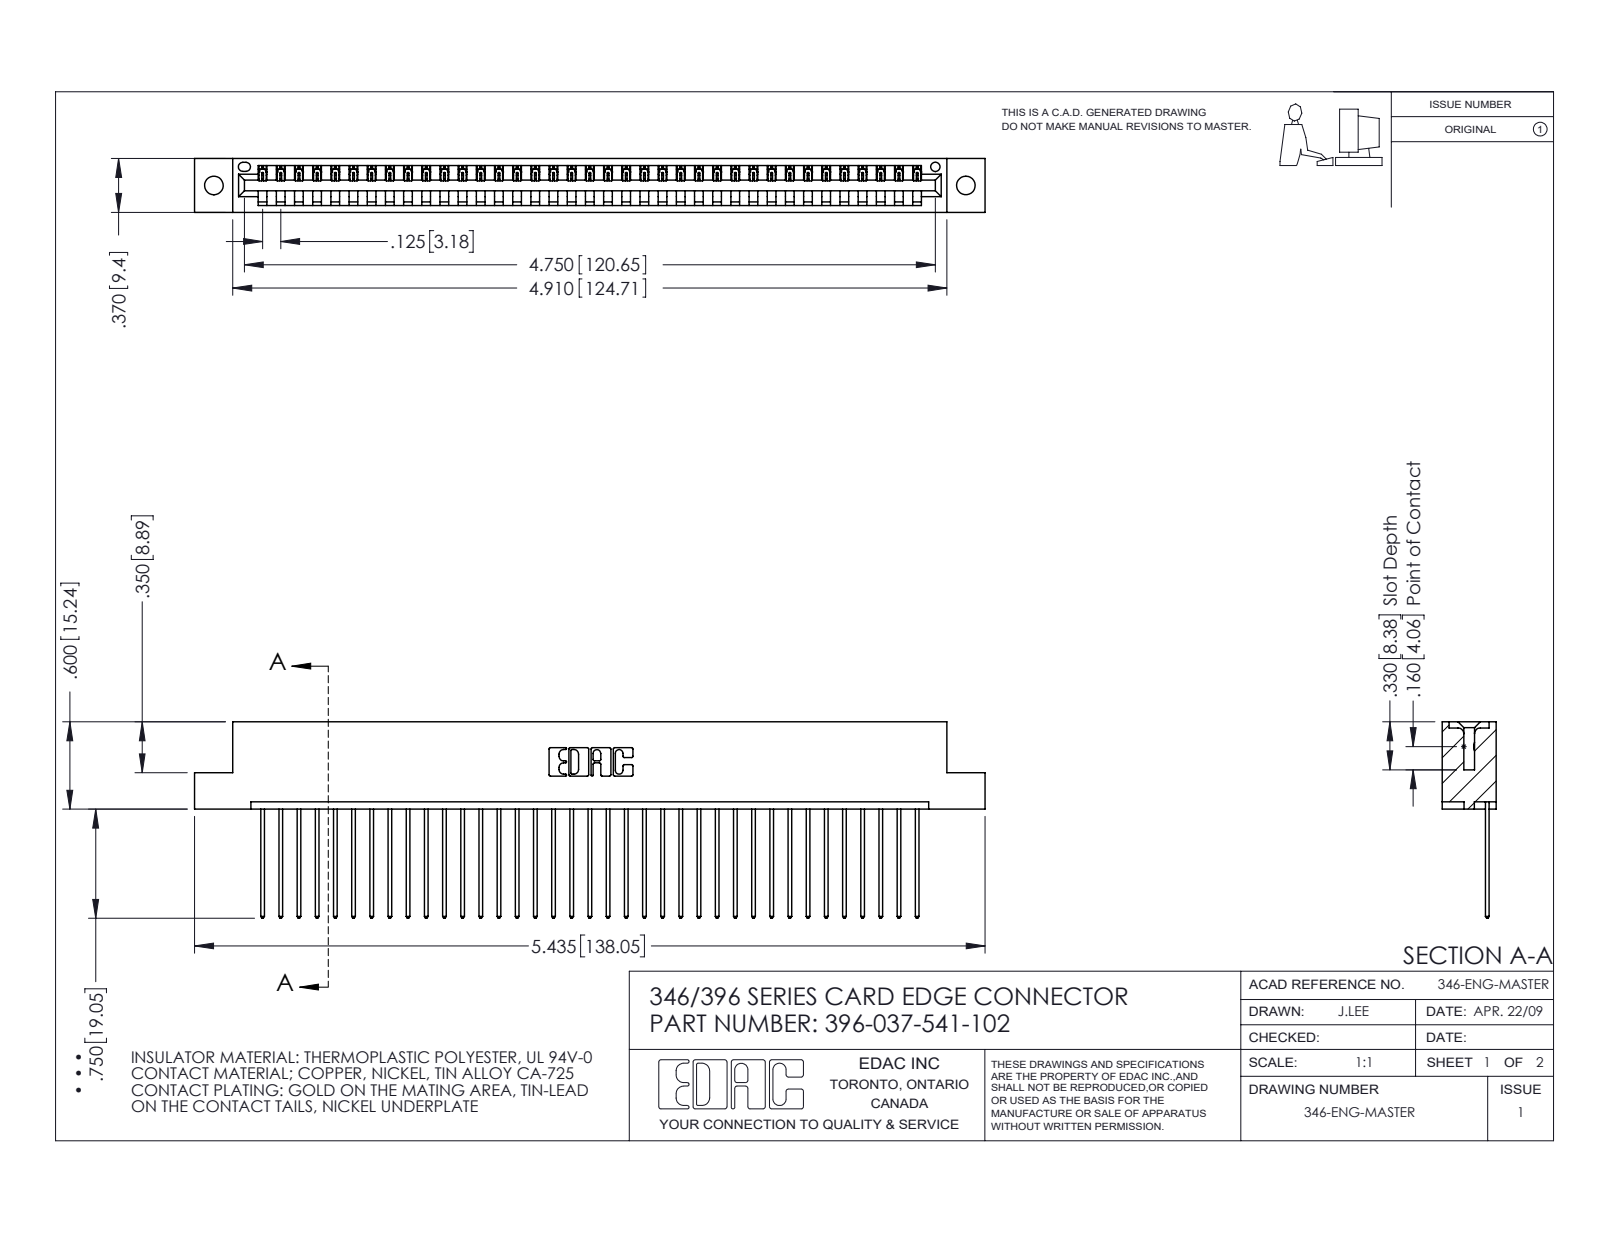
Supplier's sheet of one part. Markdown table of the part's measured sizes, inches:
| quantity | value |
| --- | --- |
| part name | 396-037-541-102; 345-292-001_345-293-141; 346 Part_Flush Mounting Lugs - 0.128 Dia |
| STEP written by | SolidWorks 2016 (CONFIG_CONTROL_DESIGN) |
| units | inches |
| bodies | 38 solids, 2268 faces (1556 planar, 712 cylindrical, 0 other) |
| overall size | 5.435 × 1.35 × 0.37 |
| volume | 0.809 in³ |
| surface area | 26.33 in² |
| round holes (diameter × count) | 0.128 × 2, 0.064 × 1 |
| partial cylindrical surfaces (radius × count) | 0.006 × 74, 0.01 × 74, 0.01 × 22, 0.007 × 6, 0.031 × 6, 0.026 × 3, 0.031 × 2, 0.04 × 2 |
| main face-to-face distances | 0.048, 0.322, 0.37, 0.25, 0.072, 0.298, 0.025, 0.148, 0.222, 0.1 |
| hole center spacings | 0.246, 4.961, 5.17 |
